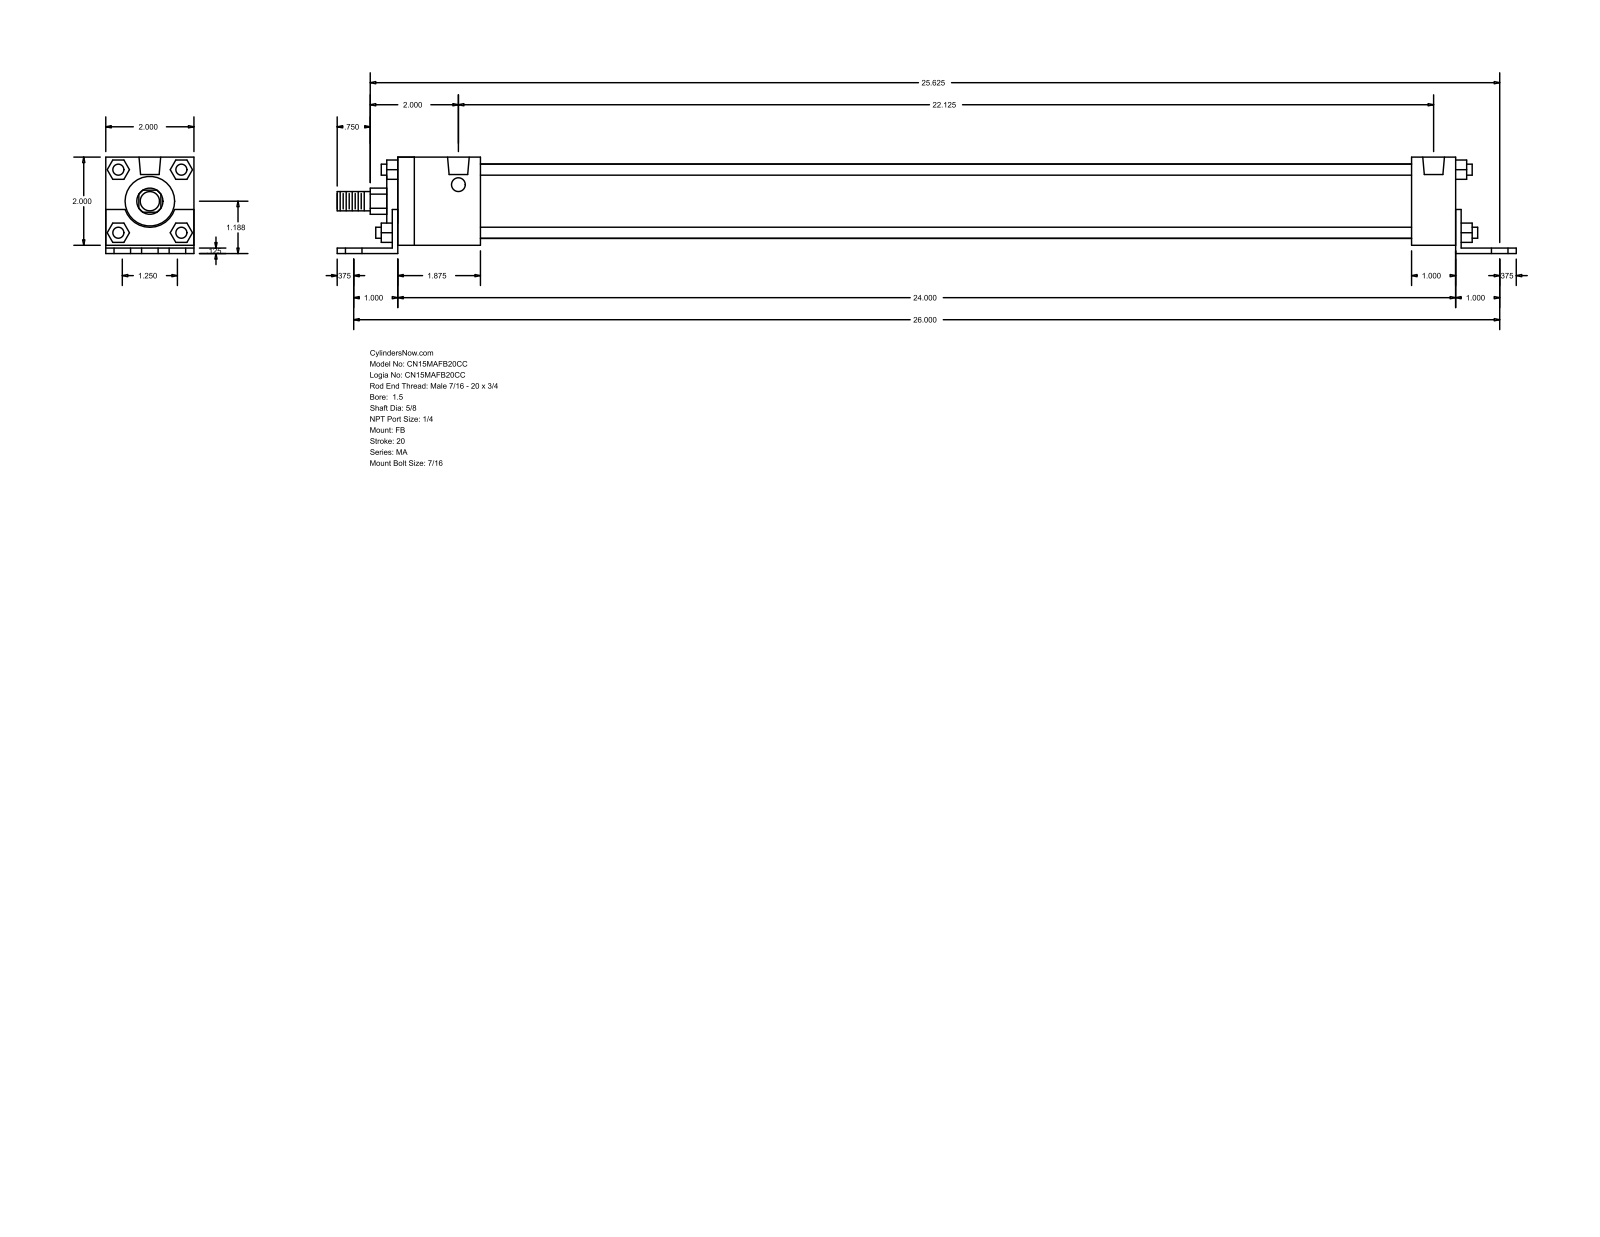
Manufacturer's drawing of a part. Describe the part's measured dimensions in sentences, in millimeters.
The part is named "MA_FB__0150_0.625". Its 3-D file was written by "GSSL Pune (CONFIG_CONTROL_DESIGN)". It is 0 solids with 140 faces: 105 planar, 35 cylindrical and 0 other. Overall it measures 679.45 by 55.56 by 50.8 millimeters. Round holes: 6 of diameter 11.11, 4 of diameter 7.94, 2 of diameter 12.49. Round bosses or shafts: 4 of diameter 6.35, 1 of diameter 42.93, 1 of diameter 28.57, 1 of diameter 15.88, 1 of diameter 11.11. Partial cylindrical surfaces (rounded edges, fillets, slot ends): 1 of radius 7.54, 1 of radius 15.05. The main face-to-face distances are 50.8, 3.17, 4.76, 55.56, 1.59, 52.39, 25.4, 615.95, 6.35, 3.18. The hole center spacings are 15.88, 660.6, 660.41, 31.76, 41.29, 62.38, 561.97, 600.29.
